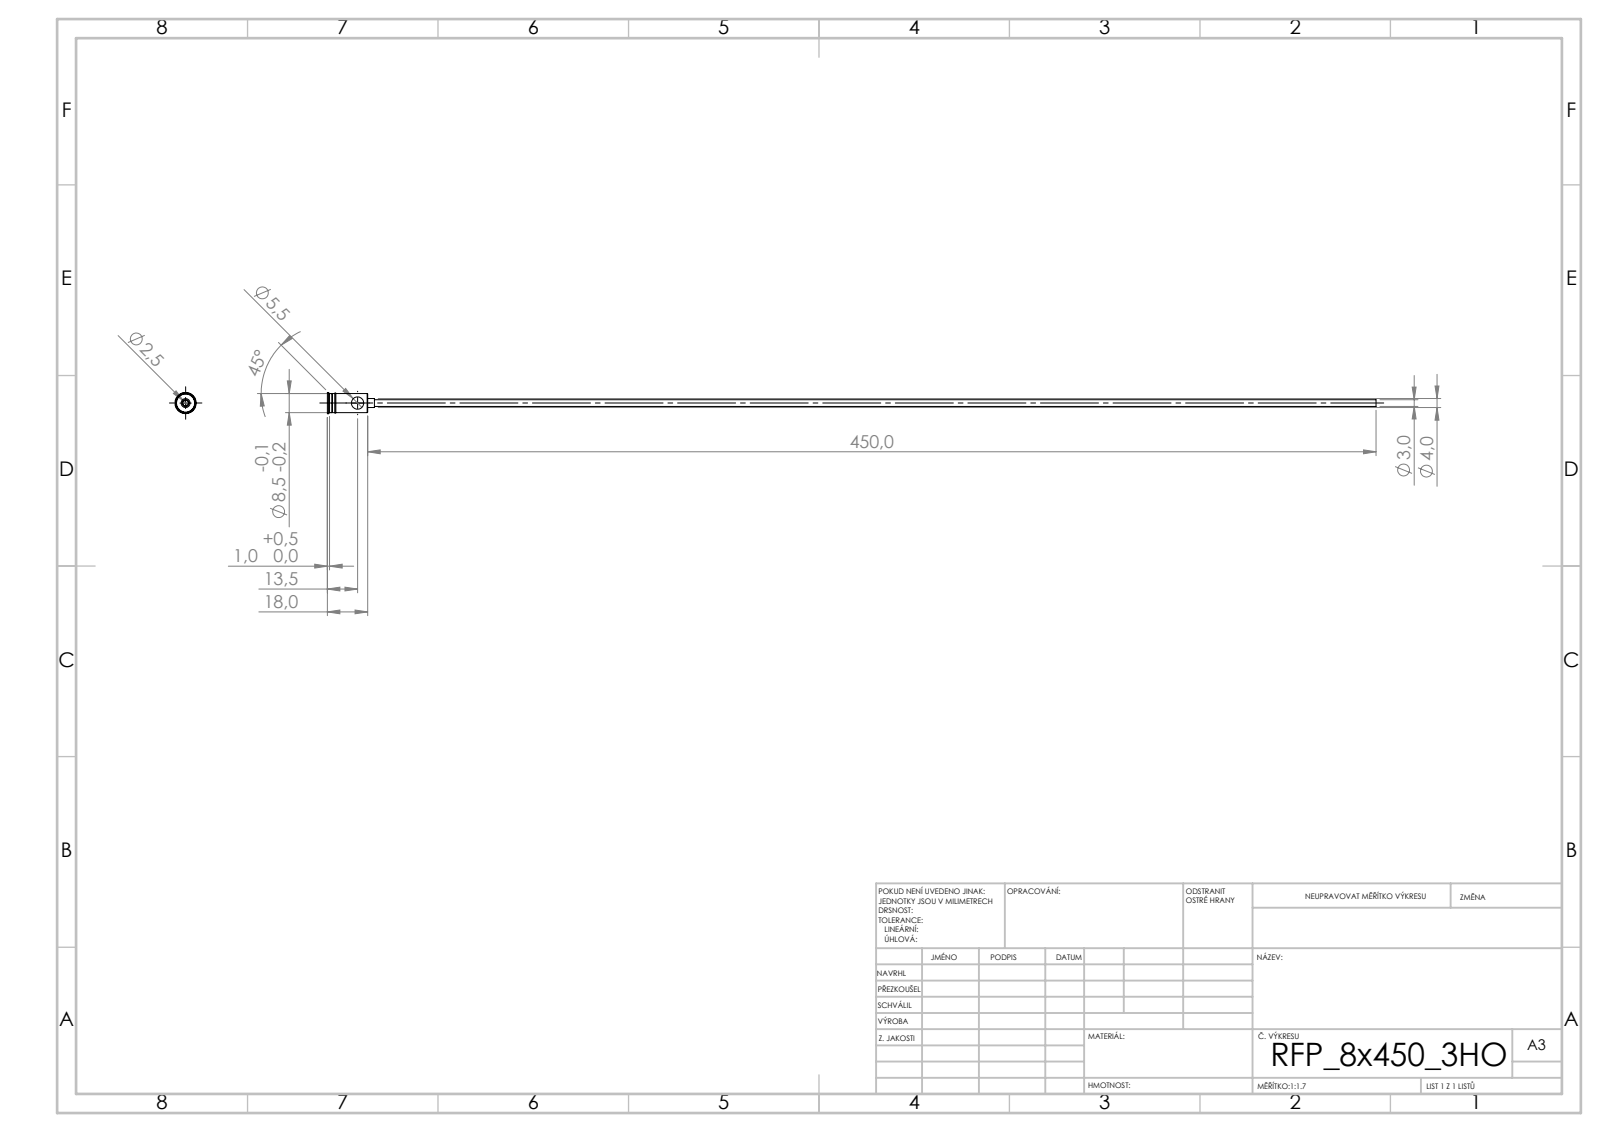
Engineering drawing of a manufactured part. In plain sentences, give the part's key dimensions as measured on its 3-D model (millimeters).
Its 3-D file was written by "SolidWorks 2019 (CONFIG_CONTROL_DESIGN)". It is 1 solid with 44 faces: 20 planar, 16 cylindrical and 8 other. Overall it measures 468 by 9.5 by 9.5 millimeters. Its volume is 1 796 cubic millimeters and its surface area 8 530 square millimeters. Round holes: 1 of diameter 2.5, 1 of diameter 5.5. Round bosses or shafts: 1 of diameter 9.5, 1 of diameter 8.5, 1 of diameter 4, 1 of diameter 3. The main face-to-face distances are 18, 16, 2, 3.9, 15.7, 2.3, 3, 18.7, 19, 21.
